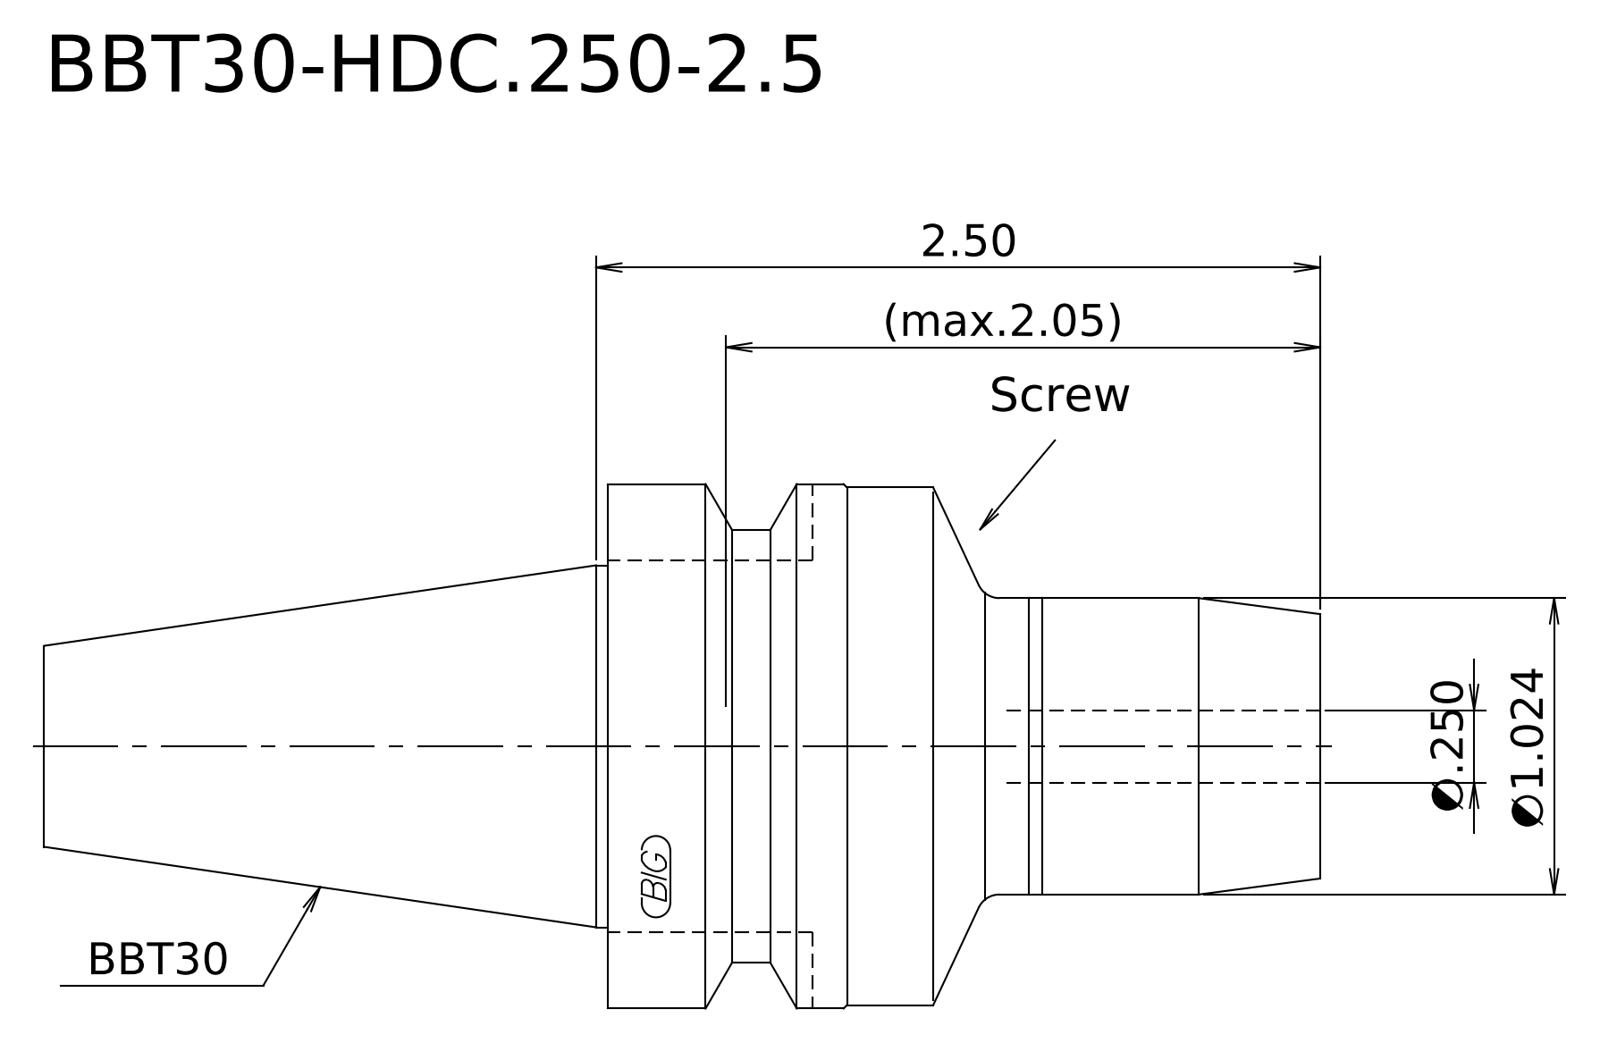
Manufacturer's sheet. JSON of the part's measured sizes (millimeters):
{"step_written_by": "Kubotek KeyCreator 2011 V10.0.2 (22737) (automotive_design)", "units": "millimeters", "bodies": {"solids": 1, "faces": 16, "planar": 3, "cylindrical": 6, "other": 7}, "overall_size": [111.9, 46, 46], "volume_mm3": 88423, "surface_area_mm2": 13562, "round_bosses_or_shafts": [[46, 1], [45.4, 1], [38, 1], [31.75, 1], [26, 1]], "face_to_face_distances": [62.5, 111.9, 49.4]}
